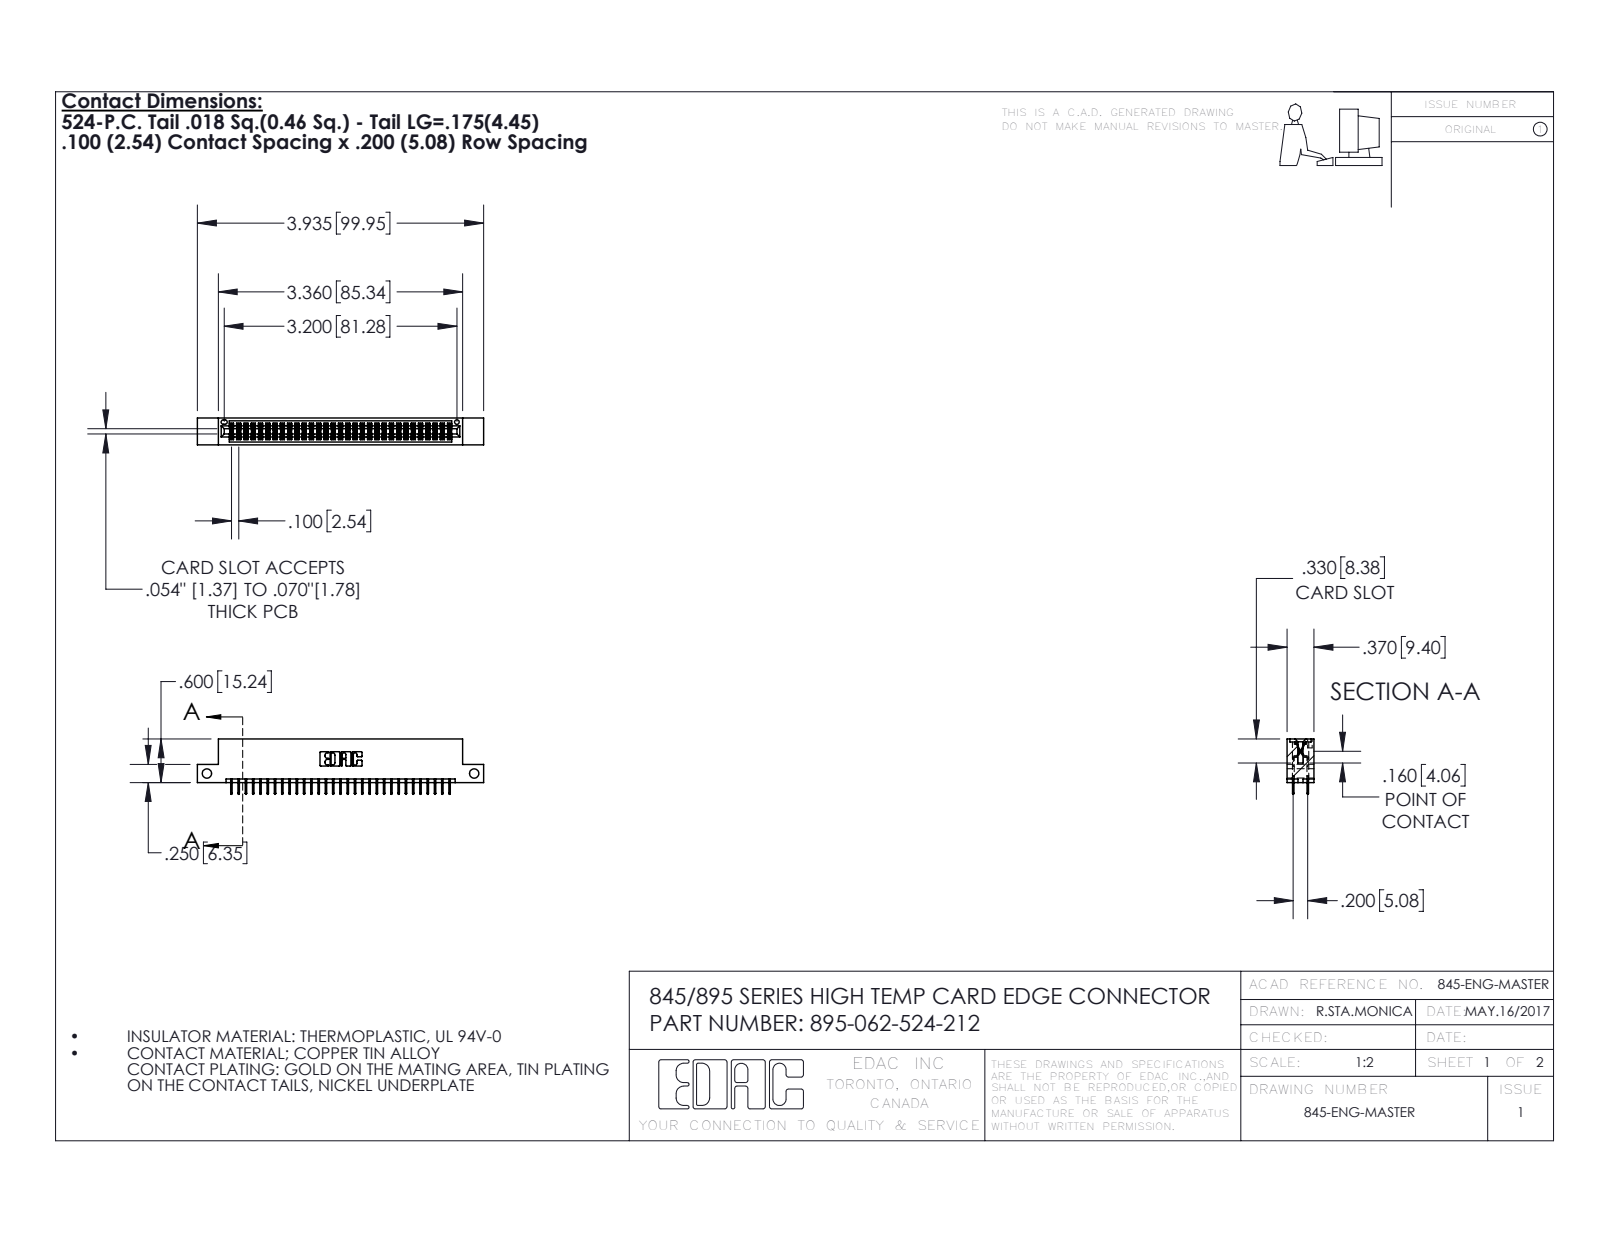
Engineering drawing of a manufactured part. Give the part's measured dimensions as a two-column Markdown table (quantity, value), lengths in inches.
| quantity | value |
| --- | --- |
| part name | 345 Part_Flush Mounting Lugs - Side Mount; 345-292-001_345-293-124; 395-062-524-212 |
| STEP written by | SolidWorks 2016 (CONFIG_CONTROL_DESIGN) |
| units | inches |
| bodies | 63 solids, 3474 faces (2498 planar, 976 cylindrical, 0 other) |
| overall size | 3.935 × 0.762 × 0.37 |
| volume | 0.575 in³ |
| surface area | 20.67 in² |
| round holes (diameter × count) | 0.128 × 2, 0.064 × 1 |
| partial cylindrical surfaces (radius × count) | 0.006 × 93, 0.01 × 22, 0.007 × 6, 0.031 × 6, 0.026 × 3, 0.014 × 2, 0.019 × 2, 0.022 × 2 |
| main face-to-face distances | 0.072, 0.298, 0.2, 0.37, 0.098, 0.272, 0.025, 0.225, 0.072, 0.175 |
| hole center spacings | 3.675 |
